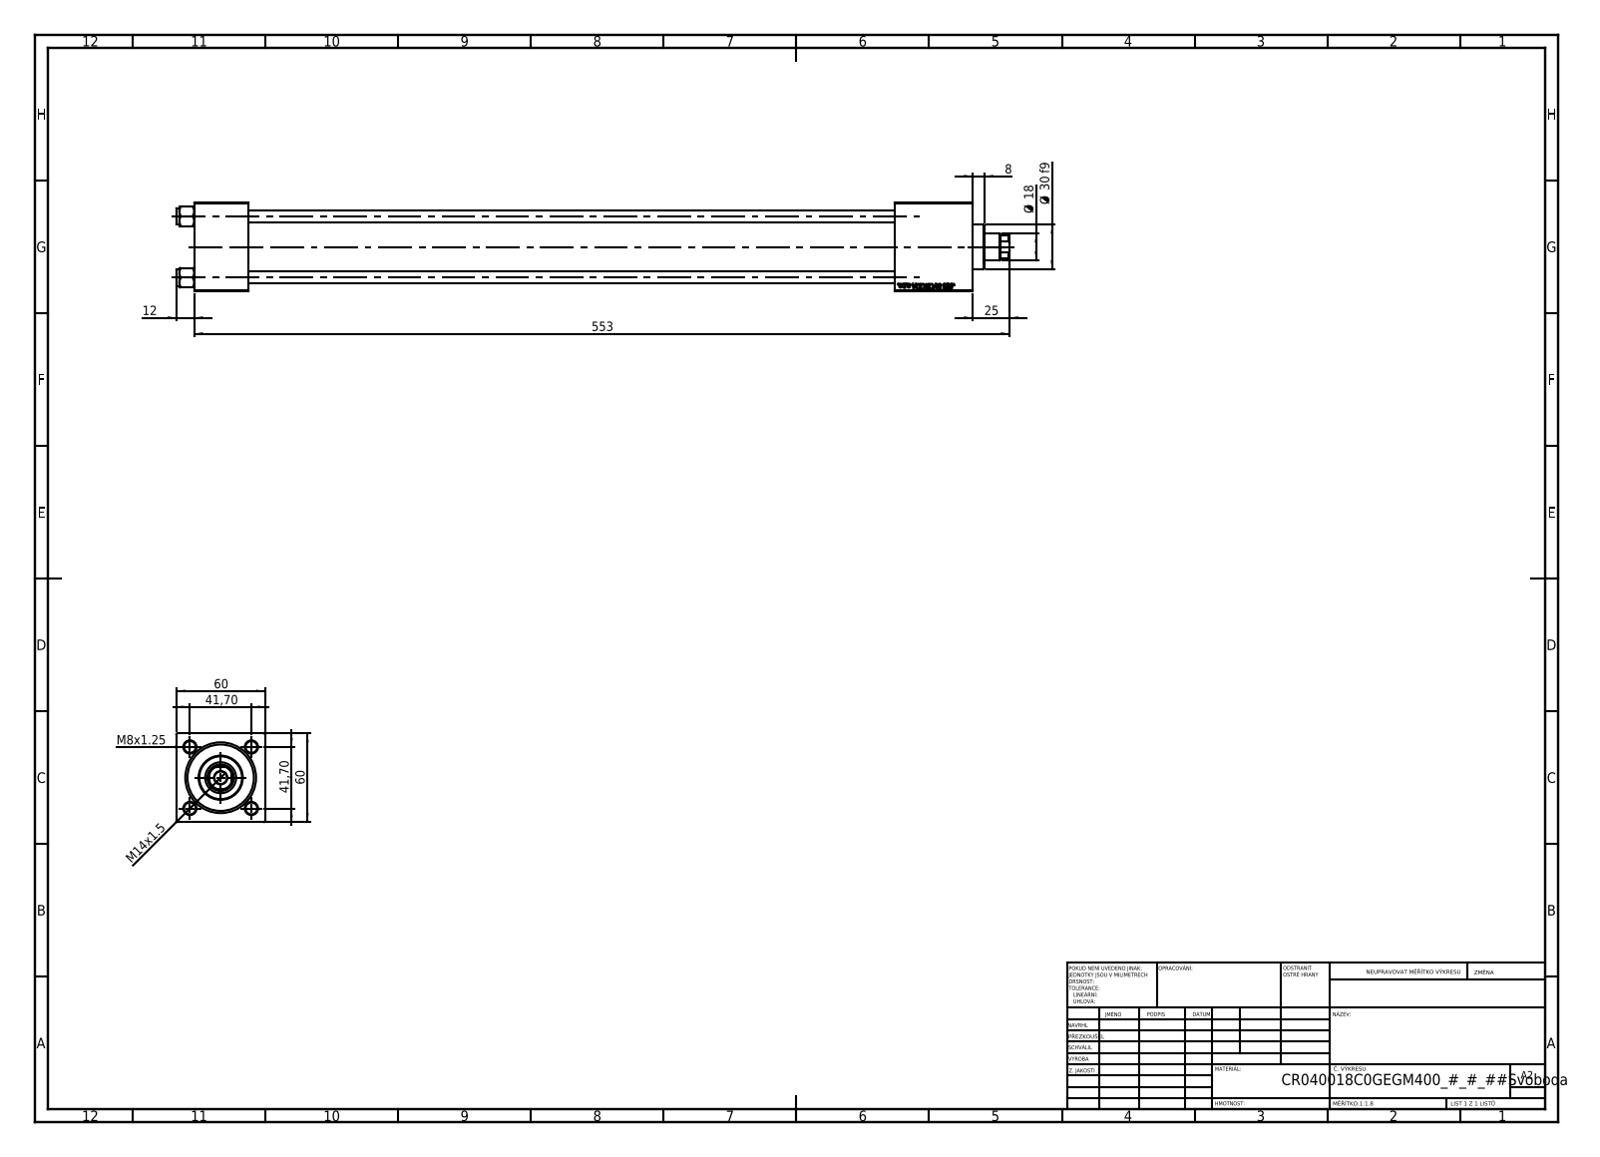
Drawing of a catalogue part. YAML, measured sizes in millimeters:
part_name: "V215CR_C_Body; NUT_M5_C; V215CR_VCP_C; V215_VC_A (+1 more)"
step_written_by: "SolidWorks 2019 (CONFIG_CONTROL_DESIGN)"
units: millimeters
bodies: {solids: 11, faces: 1149, planar: 526, cylindrical: 87, other: 536}
overall_size: [565, 60, 60]
volume: 729593
surface_area: 267686
round_holes:
  - {diameter: 8, count: 4}
  - {diameter: 7, count: 2}
  - {diameter: 16.66, count: 2}
  - {diameter: 24, count: 2}
  - {diameter: 8.5, count: 1}
  - {diameter: 18, count: 1}
  - {diameter: 21, count: 1}
  - {diameter: 31, count: 1}
  - {diameter: 40, count: 1}
  - {diameter: 45, count: 1}
round_bosses_or_shafts:
  - {diameter: 11, count: 4}
  - {diameter: 46, count: 1}
  - {diameter: 30, count: 1}
partial_cylinders:
  - {radius: 8.5, count: 1}
face_to_face_distances: [60, 37, 528, 491, 53, 475, 438, 499.3, 462.3, 24.3]
hole_center_spacings: [29.49, 41.7, 58.97, 472.5]
